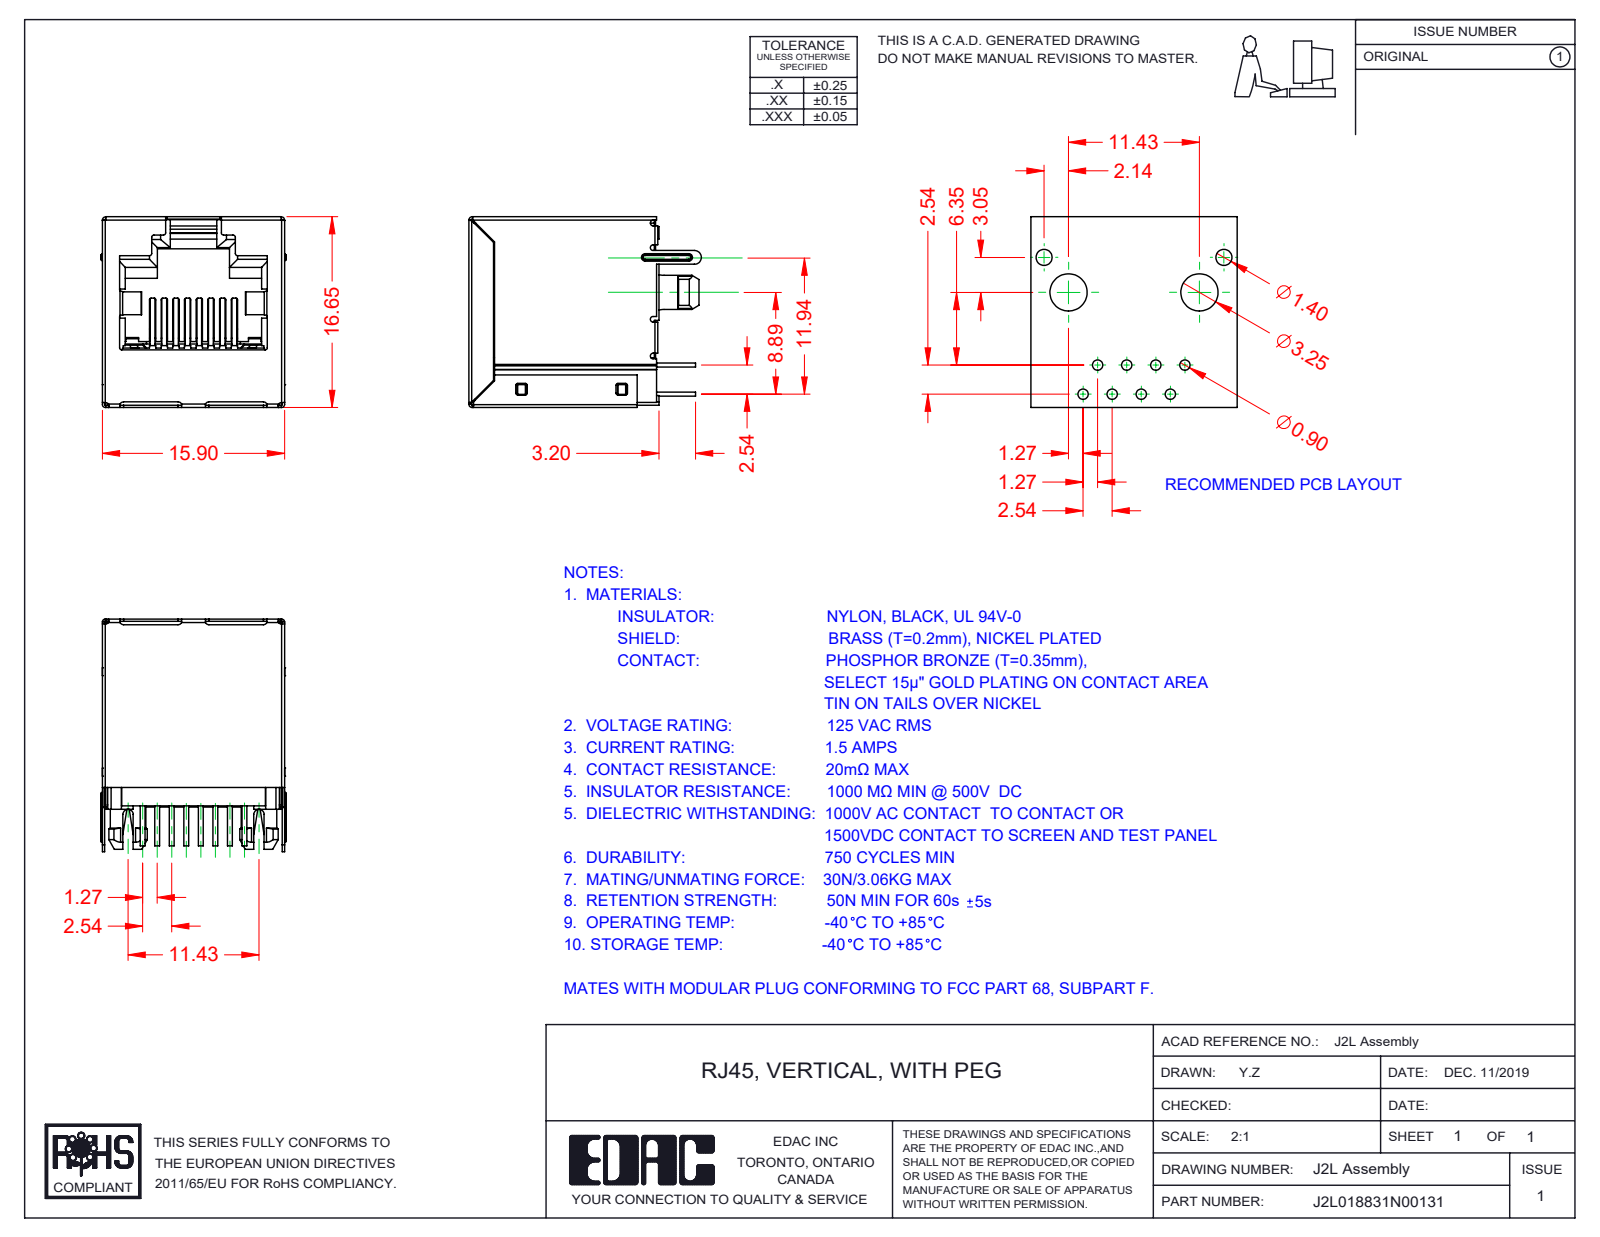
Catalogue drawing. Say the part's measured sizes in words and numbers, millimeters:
The part is named "RJ2L018831N00131; 2L Shield; 2L Contact Lock; 2L Contacts (+1 more)". Its 3-D file was written by "SolidWorks 2016 (CONFIG_CONTROL_DESIGN)". It is 11 solids with 1125 faces: 778 planar, 284 cylindrical and 63 other. Overall it measures 20.3 by 16.65 by 16.2 millimeters. Its volume is 2 717 cubic millimeters and its surface area 6 473 square millimeters. Round bosses or shafts: 2 of diameter 3.1, 2 of diameter 1.1. Partial cylindrical surfaces (rounded edges, fillets, slot ends): 64 of radius 0.15, 20 of radius 0.25, 16 of radius 0.2, 14 of radius 0.3, 9 of radius 0.35, 8 of radius 0.1, 4 of radius 0.28, 3 of radius 0.5. The main face-to-face distances are 15.45, 15.7, 16.45, 16.2, 16.4, 15.65, 16.25, 15.9, 15.5, 1.2.
